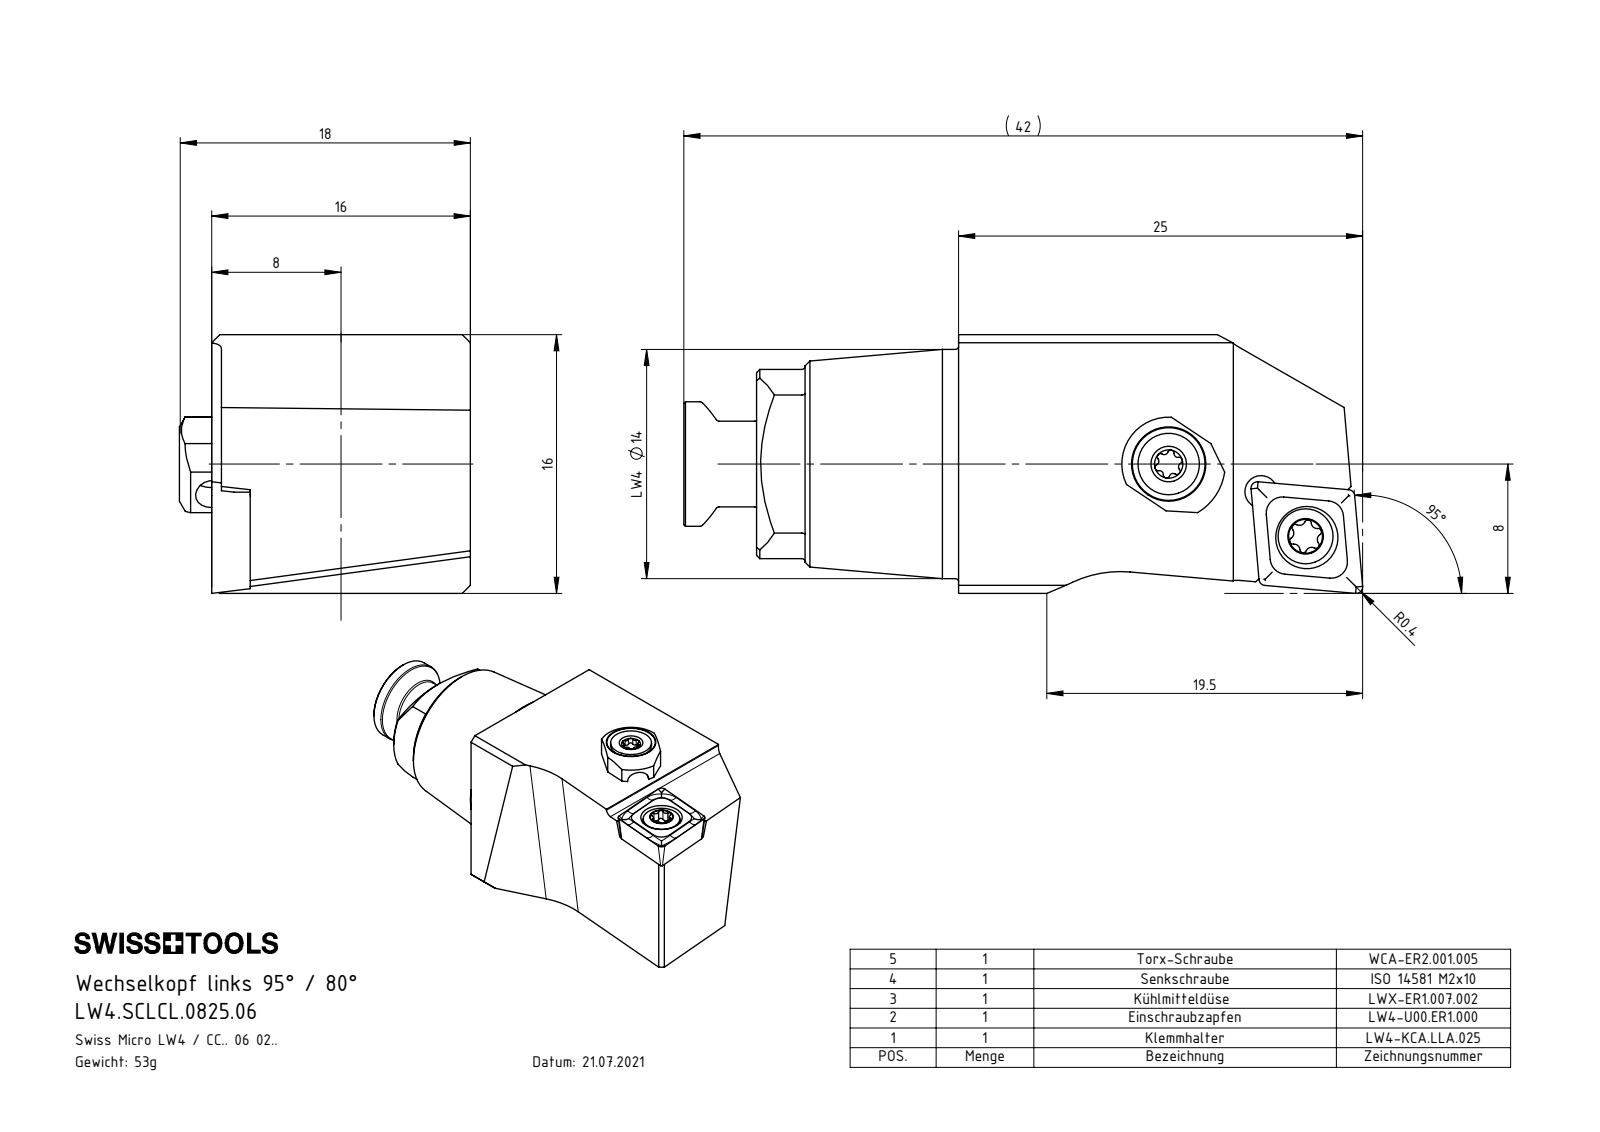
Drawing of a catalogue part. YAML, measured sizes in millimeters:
part_name: "LW4-U00.ER1.000_B; LW4.SCLCL.0825.06; CCMT060204; LWX-ER1.007.002 (+3 more)"
step_written_by: "SolidWorks 2022 (CONFIG_CONTROL_DESIGN)"
units: millimeters
bodies: {solids: 6, faces: 256, planar: 68, cylindrical: 80, other: 108}
overall_size: [42, 18, 16]
volume: 6704
surface_area: 3539
round_holes:
  - {diameter: 2, count: 2}
  - {diameter: 3, count: 2}
  - {diameter: 1.6, count: 1}
  - {diameter: 2.05, count: 1}
  - {diameter: 2.5, count: 1}
  - {diameter: 2.8, count: 1}
  - {diameter: 3.85, count: 1}
  - {diameter: 5.5, count: 1}
round_bosses_or_shafts:
  - {diameter: 14.17, count: 1}
  - {diameter: 7.7, count: 1}
  - {diameter: 6, count: 1}
  - {diameter: 5.3, count: 1}
  - {diameter: 5, count: 1}
  - {diameter: 3.8, count: 1}
  - {diameter: 3.4, count: 1}
  - {diameter: 2.5, count: 1}
partial_cylinders:
  - {radius: 0.2, count: 8}
  - {radius: 0.21, count: 6}
  - {radius: 0.24, count: 6}
  - {radius: 0.36, count: 5}
  - {radius: 0.36, count: 1}
  - {radius: 0.5, count: 1}
  - {radius: 1, count: 1}
  - {radius: 2.9, count: 1}
face_to_face_distances: [16, 13.62, 2.38, 15.4, 1.78, 0.6, 7.5, 2, 4, 12.5]
hole_center_spacings: [3.9, 4.02, 5.96, 9.58, 9.69]
